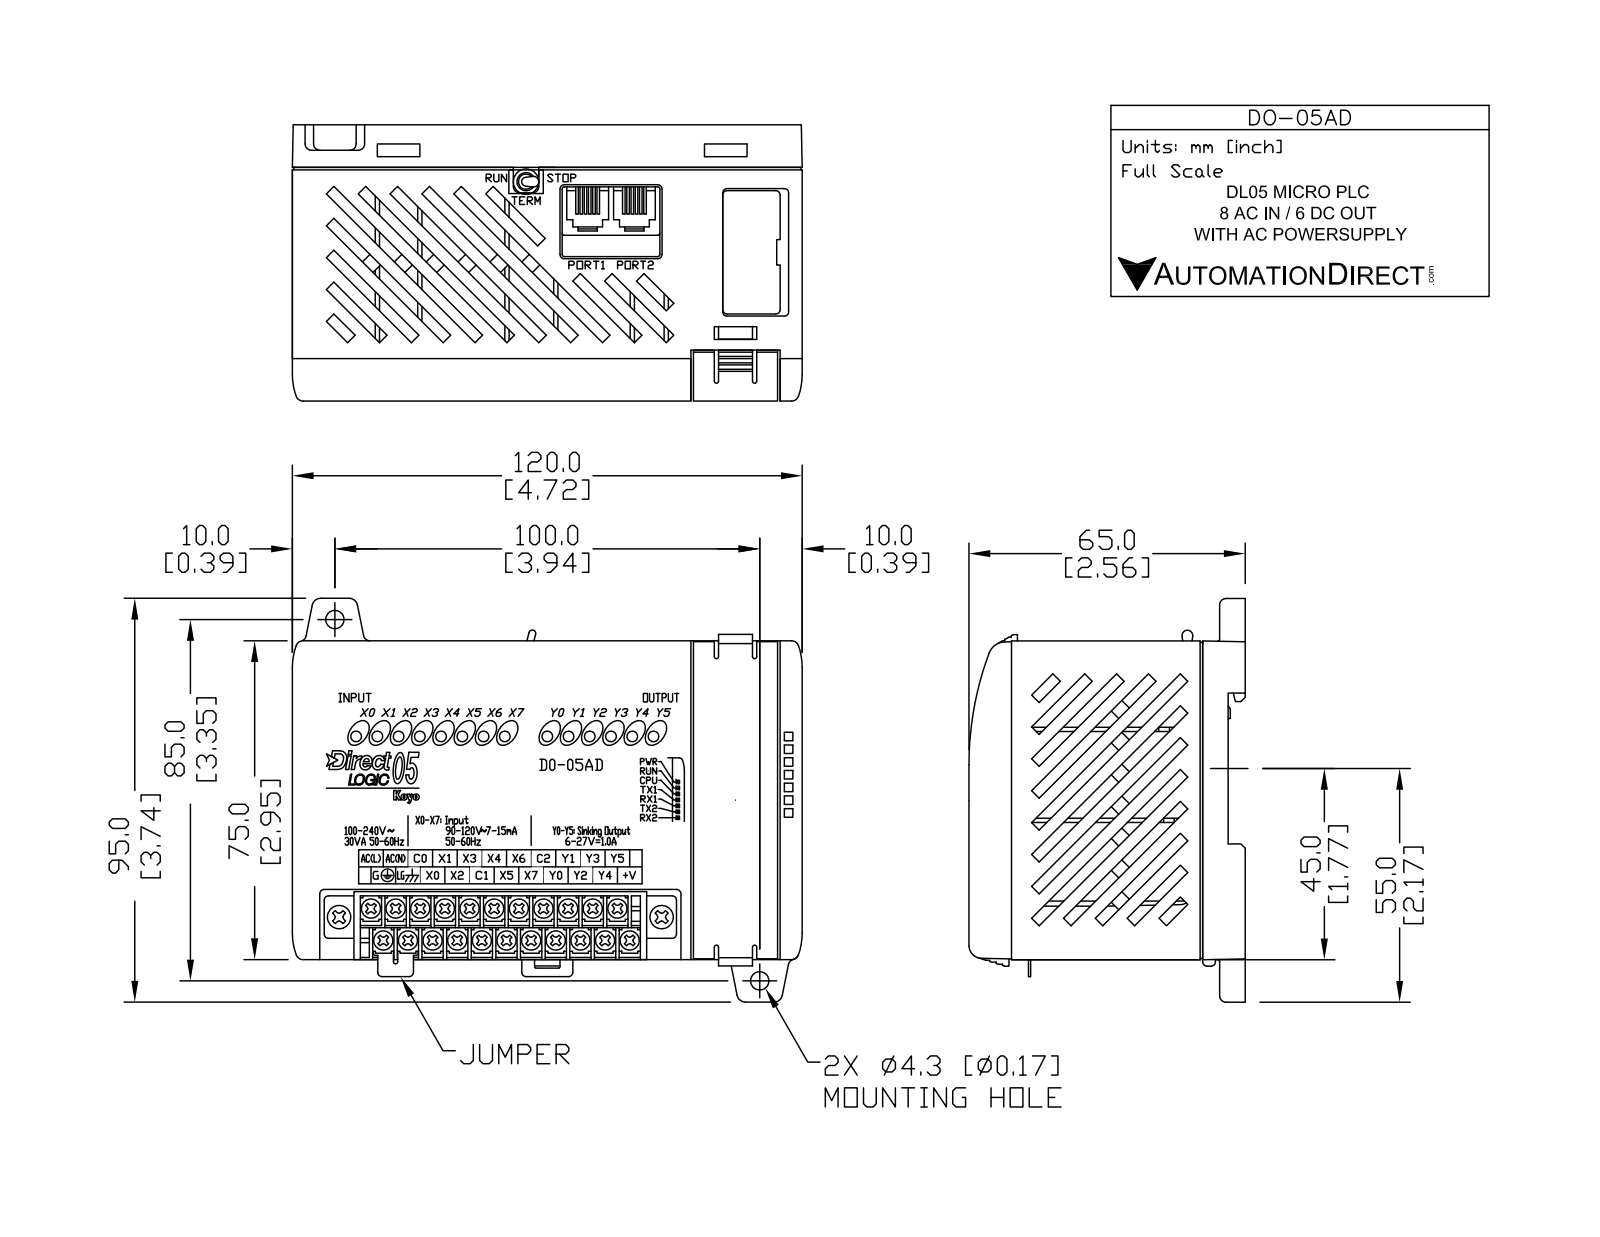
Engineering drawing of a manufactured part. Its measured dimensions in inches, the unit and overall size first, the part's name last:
Units: inches
Overall size (bounding box): 4.724 × 3.74 × 2.561
Round holes (diameter × count): ⌀0.169 ×2
Round bosses / shafts (diameter × count): ⌀0.174 ×22, ⌀0.177 ×2
Partial cylindrical surfaces — rounded edges, fillets, slot ends (radius × count): R0.039 ×4, R0.079 ×4, R0.059 ×2, R2.5 ×1, R2.559 ×1
Main face-to-face distances: 0.059, 2.894, 2.343, 0.157, 2.5, 4.665, 2.953, 2.835, 0.217, 2.559
Hole centre spacings: 5.167
Volume: 3.992 in³ · Surface area: 141.1 in²
Bodies: 3 solids, 982 faces (676 planar, 95 cylindrical, 211 other)
Part name (STEP PRODUCT): D0-05AD
STEP written by: SolidWorks 2009 (AUTOMOTIVE_DESIGN)
